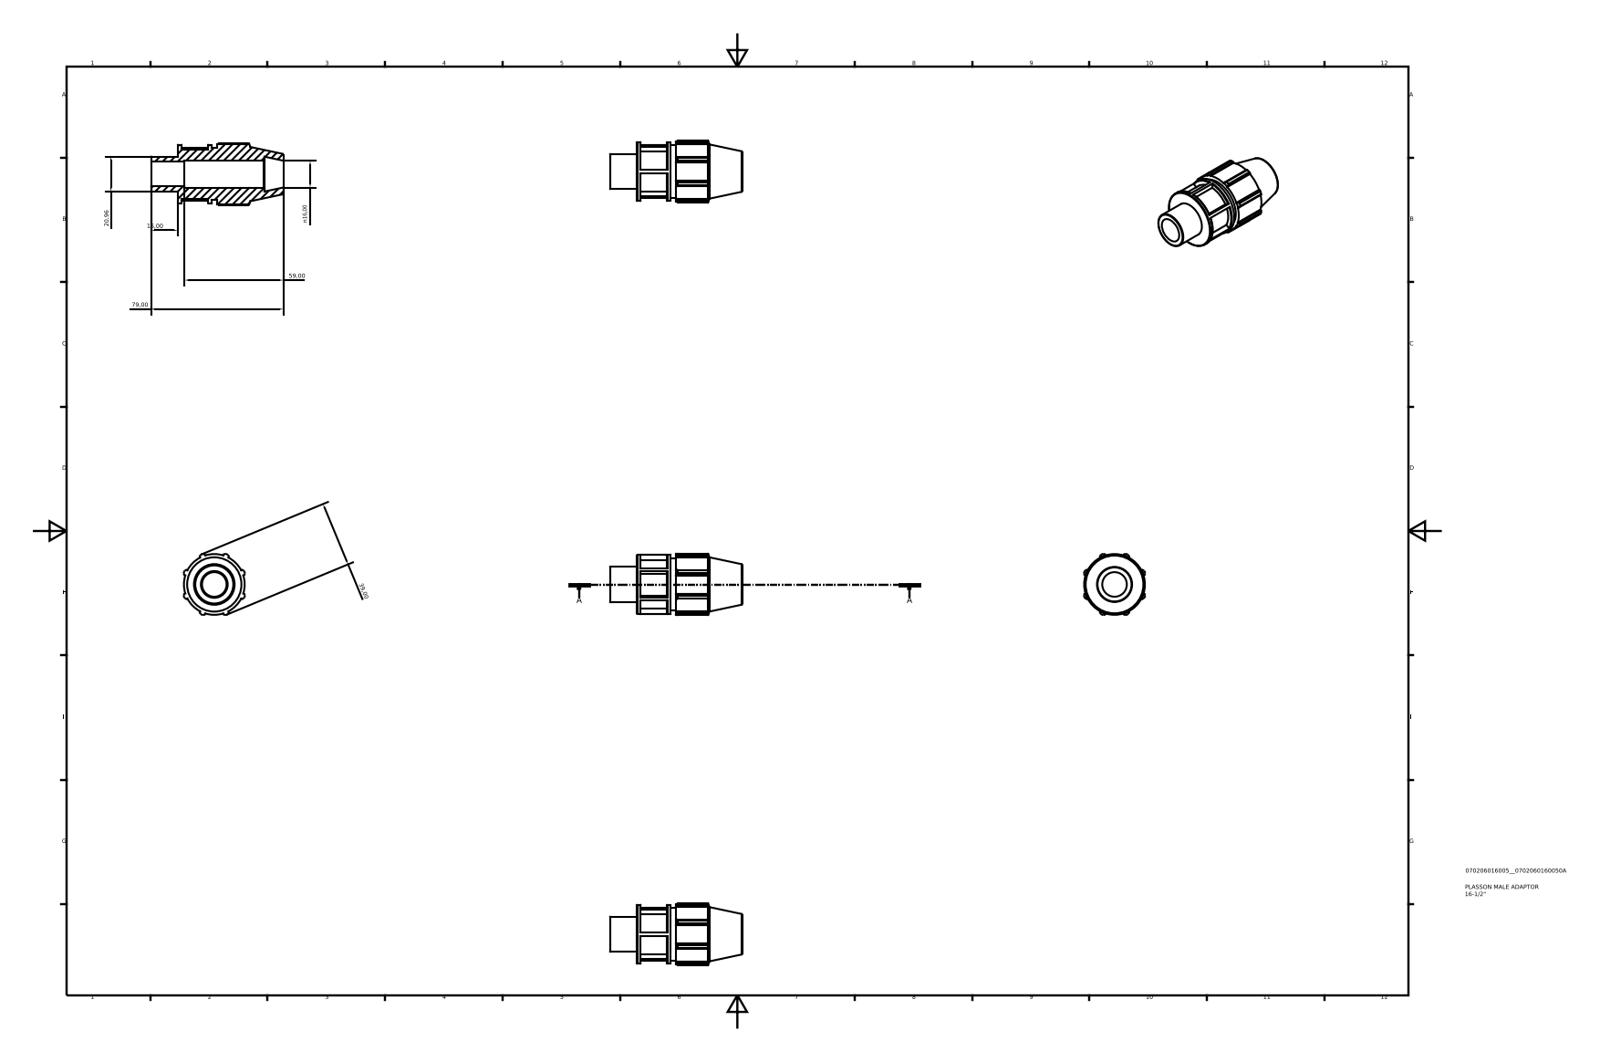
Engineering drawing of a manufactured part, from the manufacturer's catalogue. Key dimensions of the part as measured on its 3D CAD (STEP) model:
Part name (STEP PRODUCT): 070206016005
STEP written by: Autodesk Inventor 2015 (AUTOMOTIVE_DESIGN)
Units: millimetres
Bodies: 1 solid, 117 faces (63 planar, 27 cylindrical, 27 other)
Overall size (bounding box): 79 × 36.7 × 36.7
Volume: 40 805 mm³ · Surface area: 14 520 mm²
Round holes (diameter × count): ⌀14.67 ×1, ⌀16 ×1
Round bosses / shafts (diameter × count): ⌀35.1 ×1, ⌀31.2 ×1, ⌀29.25 ×1, ⌀20.95 ×1
Partial cylindrical surfaces — rounded edges, fillets, slot ends (radius × count): R18.14 ×1, R19.5 ×1
Main face-to-face distances: 39.5, 1.95, 23.5, 18.06, 5.44, 2.26, 15.8, 21.24, 63, 60.74
